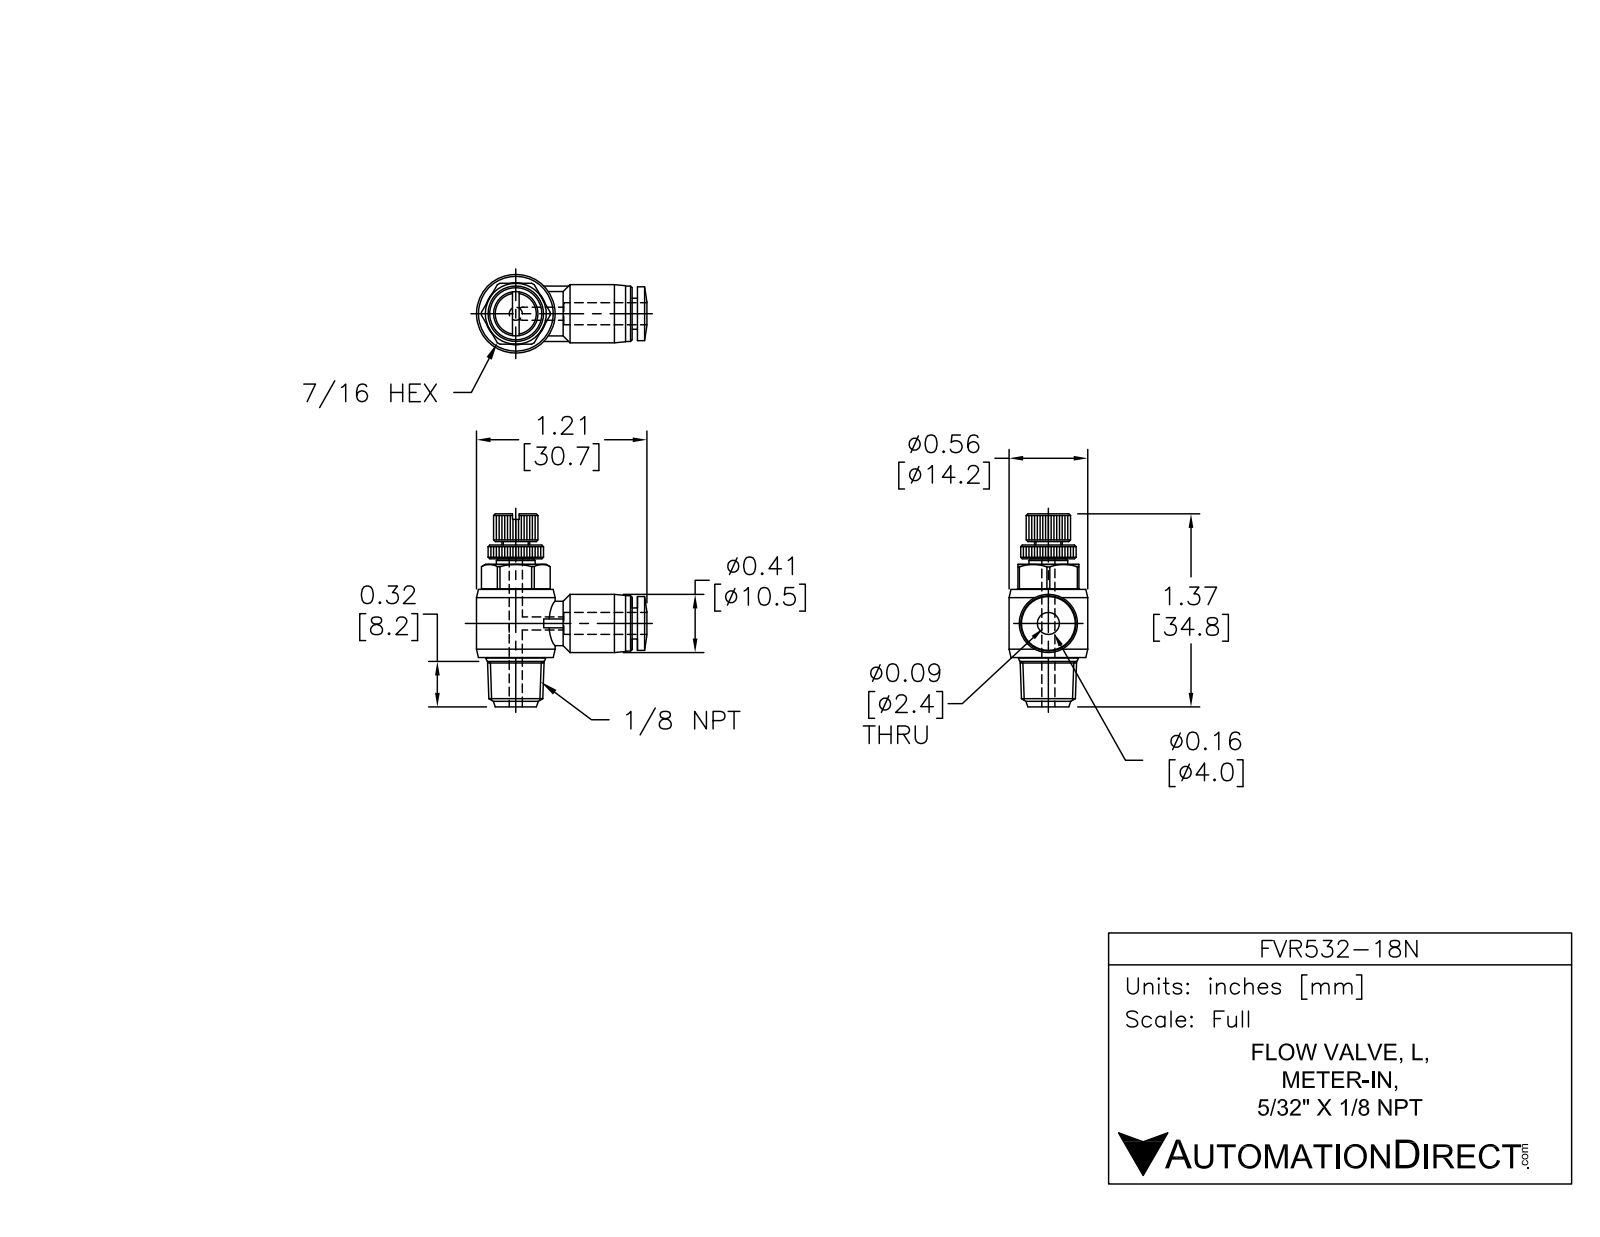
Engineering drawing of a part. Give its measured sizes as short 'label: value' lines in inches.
name: FVR532-18N
written by: SolidWorks 2015 (AUTOMOTIVE_DESIGN)
unit: in
bodies: 1 solid, 505 faces (199 planar, 112 cylindrical, 194 other)
size: 1.567 × 1.211 × 0.559
volume: 0.275 in³; area: 4.424 in²
holes: 2× ⌀0.118, 1× ⌀0.169
bosses: 1× ⌀0.559, 1× ⌀0.441, 1× ⌀0.413, 1× ⌀0.406, 1× ⌀0.394, 1× ⌀0.388, 1× ⌀0.315, 1× ⌀0.276
rounds: 1× R0.157, 1× R0.197, 1× R0.244
face distances: 0.433, 0.661, 0.206, 0.799, 0.138, 0.039, 0.037, 0.484, 0.177, 0.315
